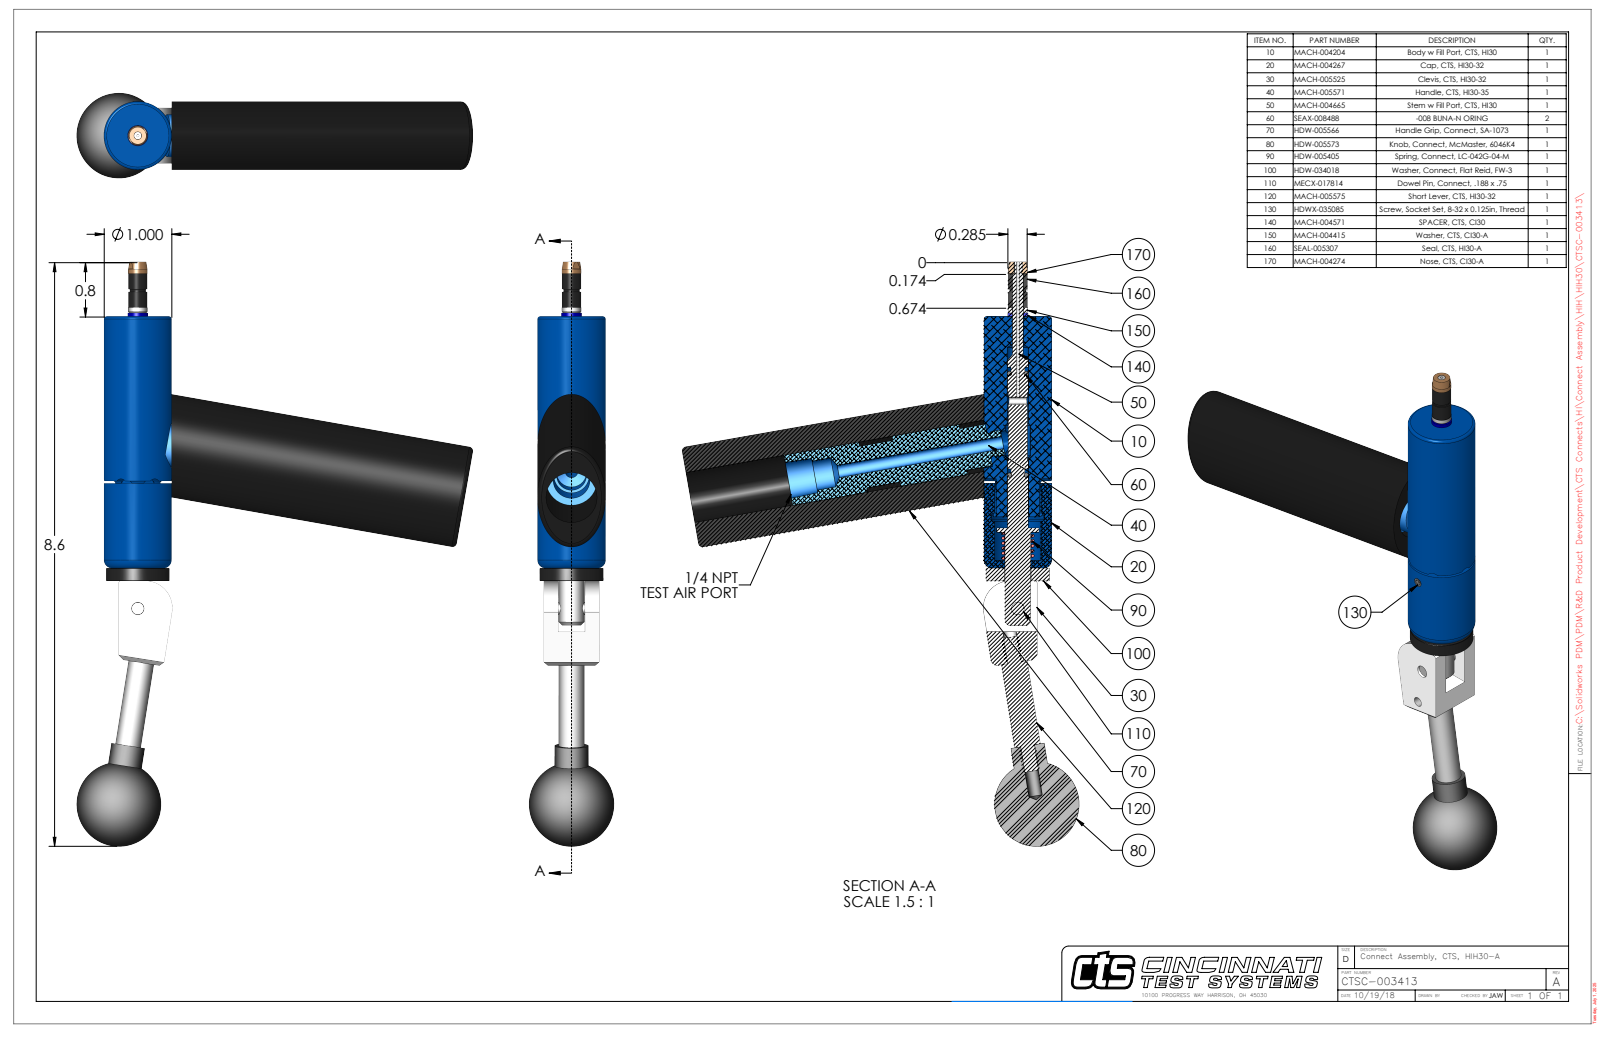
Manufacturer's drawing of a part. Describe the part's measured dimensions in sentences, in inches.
The part is named "CTSC-003413". Its 3-D file was written by "SolidWorks 2023 (AUTOMOTIVE_DESIGN)". It is 12 solids with 293 faces: 100 planar, 127 cylindrical and 66 other. Overall it measures 8.63 by 5.856 by 1.25 inches. Its volume is 9.11 cubic inches and its surface area 72.45 square inches. Round holes: 2 of diameter 0.201, 1 of diameter 0.04, 1 of diameter 0.101, 1 of diameter 0.113, 1 of diameter 0.136, 1 of diameter 0.15, 1 of diameter 0.155, 1 of diameter 0.161, 1 of diameter 0.164, 1 of diameter 0.187, 1 of diameter 0.189, 1 of diameter 0.385. Round bosses or shafts: 1 of diameter 1, 1 of diameter 0.936, 1 of diameter 0.75, 1 of diameter 0.62, 1 of diameter 0.5, 1 of diameter 0.38, 1 of diameter 0.375, 1 of diameter 0.3. Partial cylindrical surfaces (rounded edges, fillets, slot ends): 6 of radius 0.093, 1 of radius 0.015, 1 of radius 0.054, 1 of radius 0.325, 1 of radius 0.4, 1 of radius 0.46. The main face-to-face distances are 0.21, 0.602, 0.812, 0.187, 3.717, 3.904, 0.785, 0.391, 2.463, 1.253. The hole center spacings are 0.599, 1.658, 2.252.
